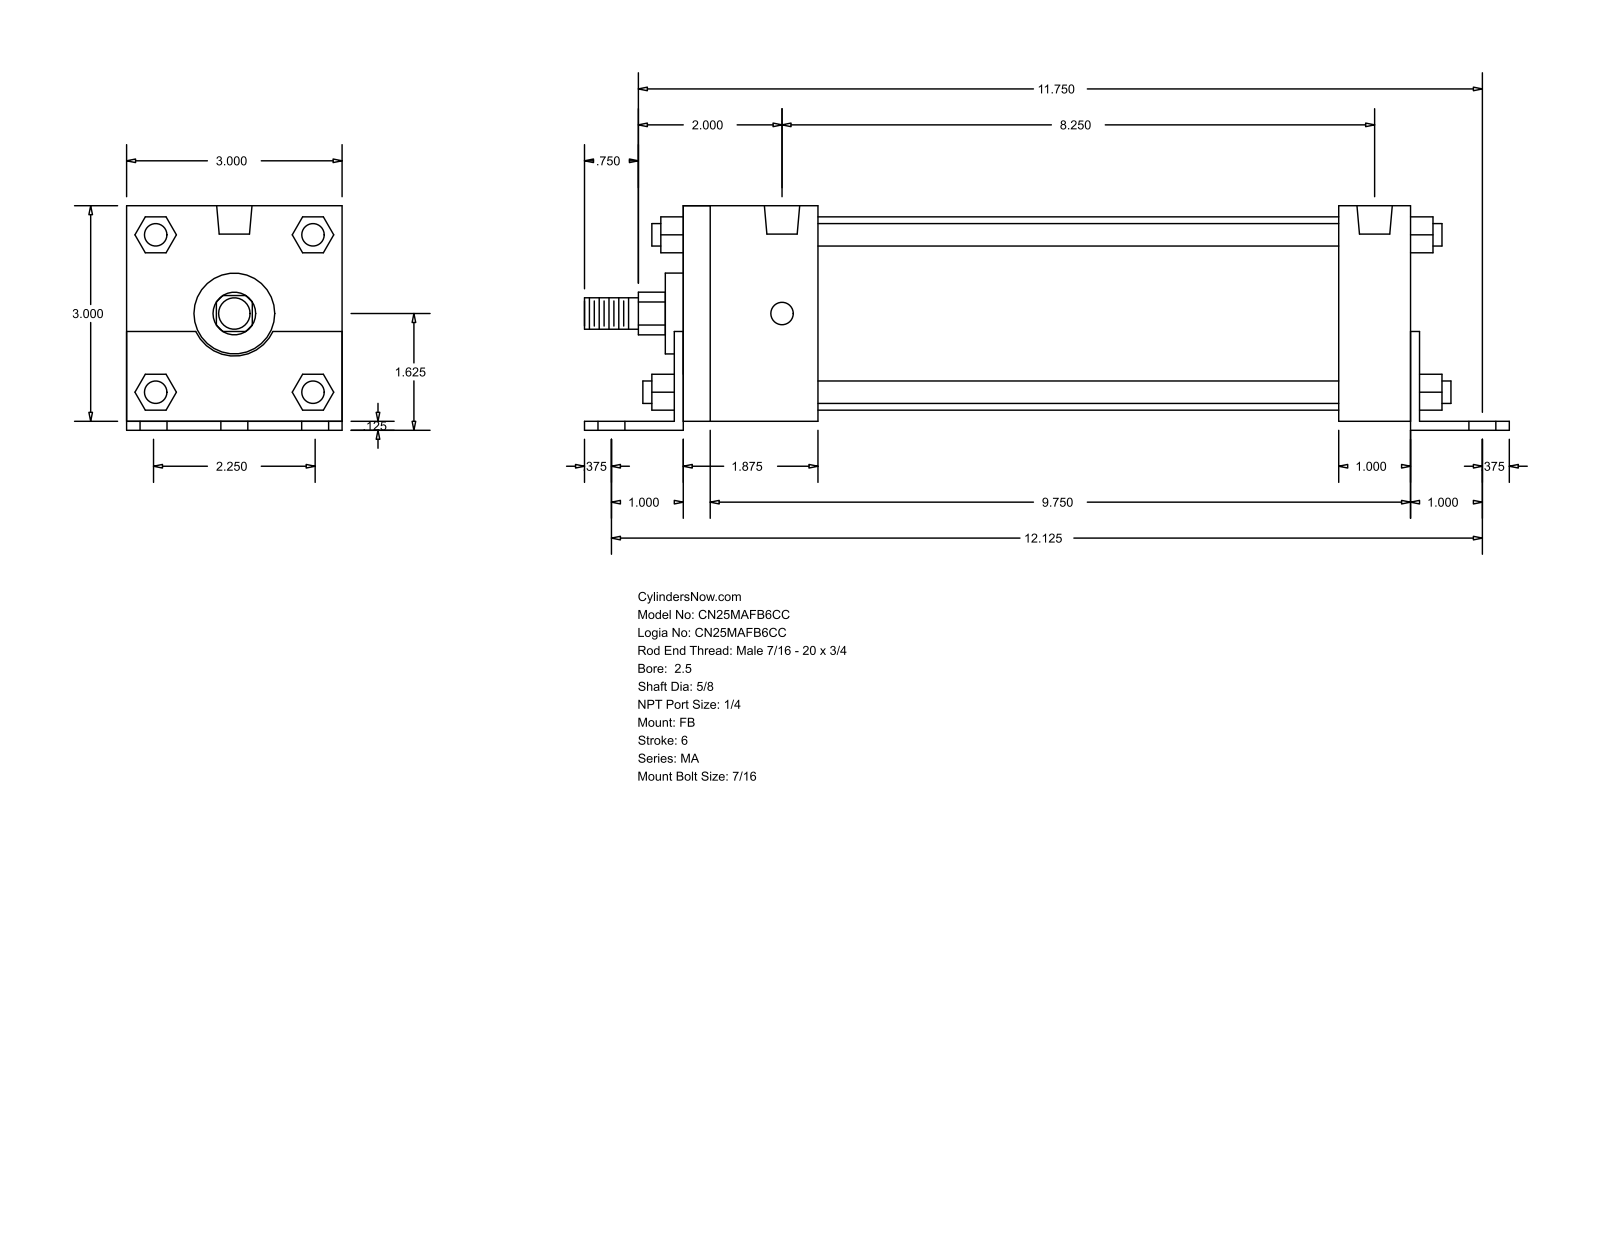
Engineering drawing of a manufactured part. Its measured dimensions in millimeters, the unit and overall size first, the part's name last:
Units: millimetres
Overall size (bounding box): 327.02 × 79.38 × 76.2
Round holes (diameter × count): ⌀11.11 ×6, ⌀7.94 ×4, ⌀12.49 ×2
Round bosses / shafts (diameter × count): ⌀7.94 ×4, ⌀68.33 ×1, ⌀28.57 ×1, ⌀15.88 ×1, ⌀11.11 ×1
Partial cylindrical surfaces — rounded edges, fillets, slot ends (radius × count): R7.54 ×1, R15.05 ×1
Main face-to-face distances: 76.2, 3.17, 79.37, 3.18, 260.35, 257.17, 28.58, 47.62, 25.4, 263.53
Hole centre spacings: 28.57, 309.3, 307.98, 47.62, 57.14, 66.75, 209.55, 249.29
Bodies: 0 solids, 140 faces (105 planar, 35 cylindrical, 0 other)
Part name (STEP PRODUCT): MA_FB__0250_0.625
STEP written by: GSSL Pune (CONFIG_CONTROL_DESIGN)
